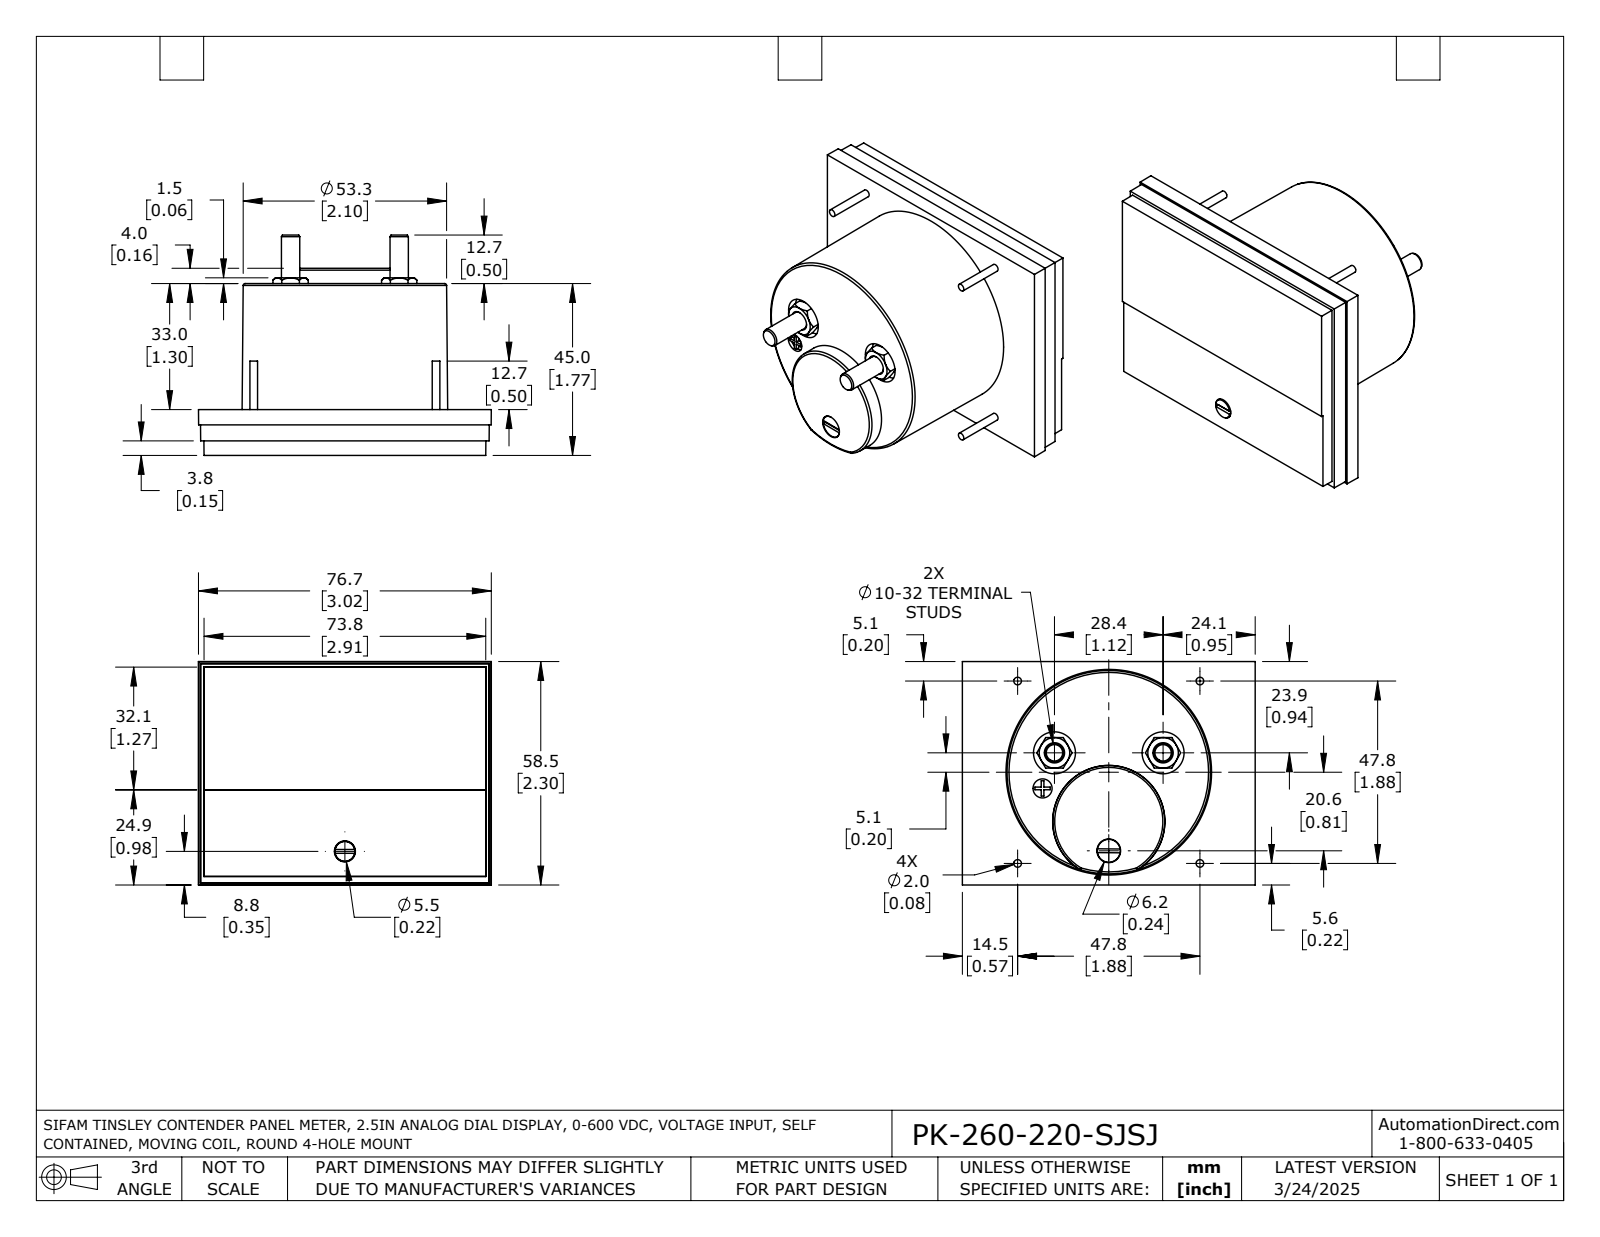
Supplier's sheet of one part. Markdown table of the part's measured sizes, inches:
| quantity | value |
| --- | --- |
| part name | PK-260-220-SJSJ |
| STEP written by | SolidWorks 2021 (AUTOMOTIVE_DESIGN) |
| units | inches |
| bodies | 1 solid, 192 faces (95 planar, 37 cylindrical, 60 other) |
| overall size | 3.02 × 2.303 × 2.272 |
| volume | 7.657 in³ |
| surface area | 36.55 in² |
| round holes (diameter × count) | 0.197 × 3, 0.433 × 2, 0.209 × 1, 0.217 × 1, 0.244 × 1 |
| round bosses / shafts (diameter × count) | 0.079 × 4, 0.189 × 2, 0.236 × 1, 0.205 × 1 |
| partial cylindrical surfaces (radius × count) | 0.033 × 1 |
| main face-to-face distances | 0.02, 0.472, 0.13, 0.322, 0.15, 0.453, 0.057, 0.077, 0.396, 0.073 |
| hole center spacings | 1.155, 1.16, 0.387, 0.938, 0.942, 1.12, 1.295 |
